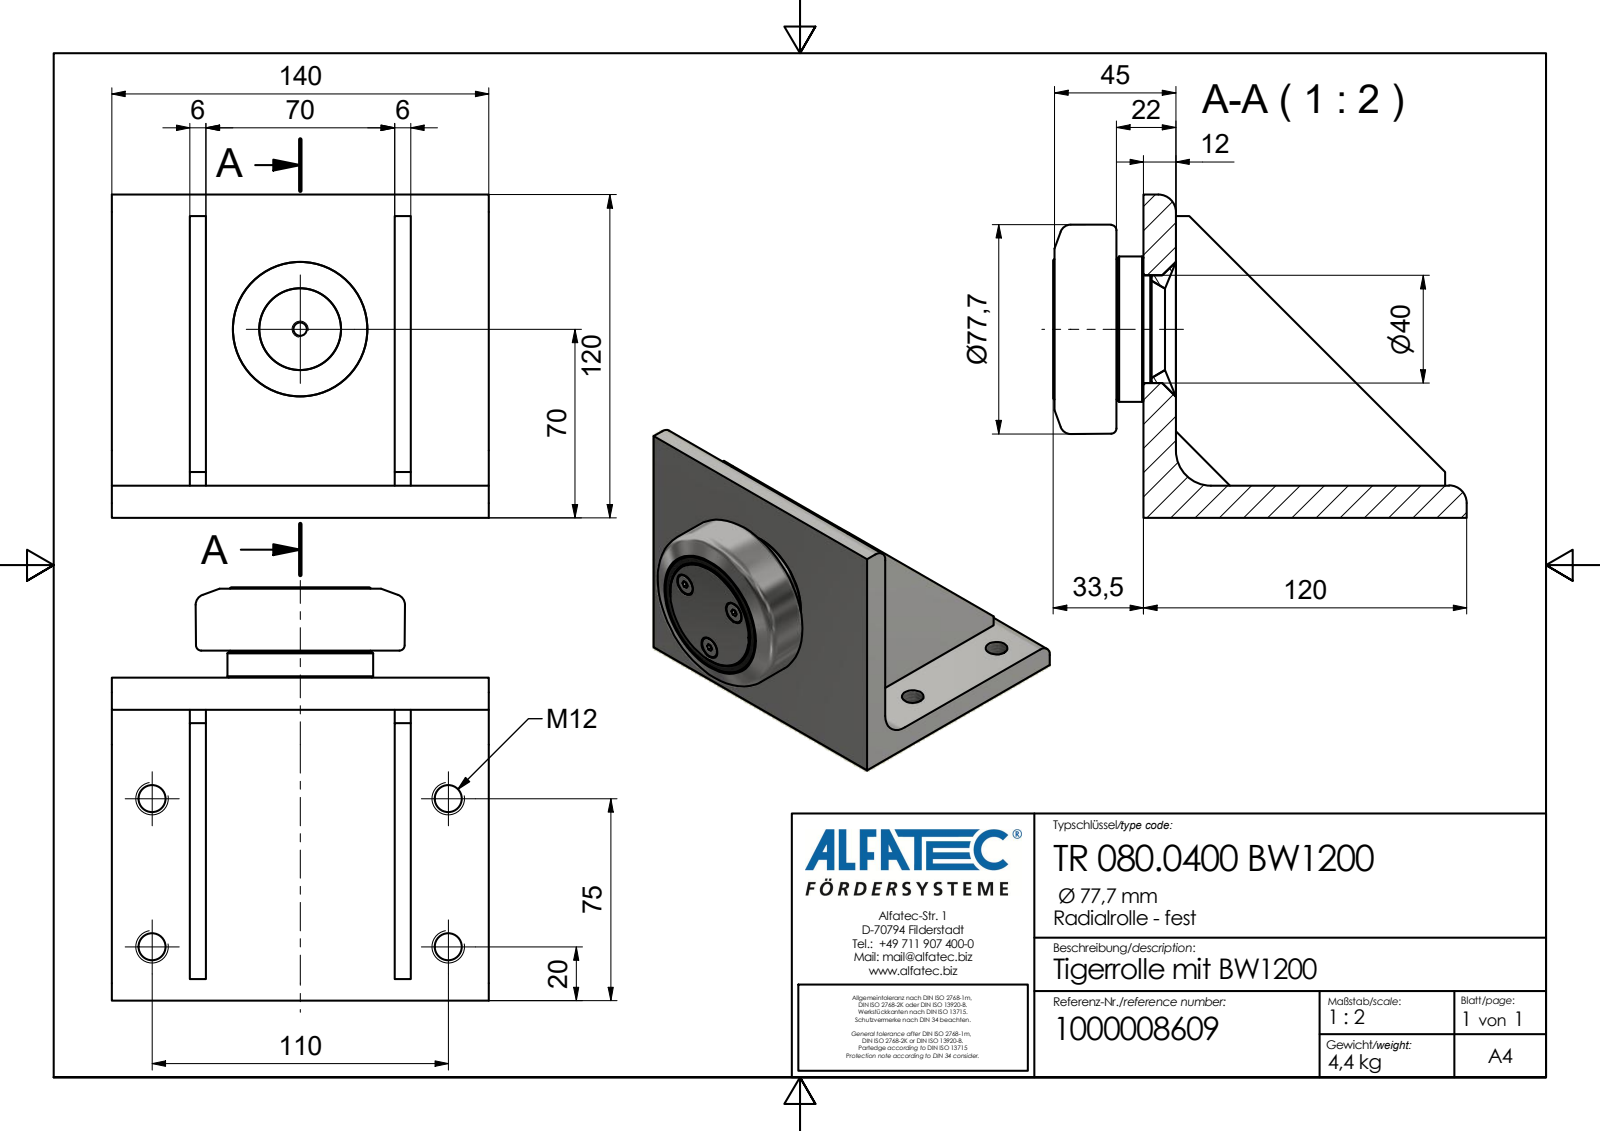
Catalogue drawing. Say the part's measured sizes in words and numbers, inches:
The part is named "TR 080.0400 BW1200_Kontur". Its 3-D file was written by "Autodesk Inventor 2020 (AP242_MANAGED_MODEL_BASED_3D_ENGINEERING_MIM_LF)". It is 1 solid with 78 faces: 53 planar, 17 cylindrical and 8 other. Overall it measures 6.043 by 5.512 by 4.724 inches. Its volume is 34.7 cubic inches and its surface area 163.4 square inches. Round holes: 4 of diameter 0.398, 3 of diameter 0.409, 1 of diameter 0.194. Round bosses or shafts: 3 of diameter 0.384, 1 of diameter 2.126, 1 of diameter 2.047. Partial cylindrical surfaces (rounded edges, fillets, slot ends): 2 of radius 0.256, 1 of radius 0.512. The main face-to-face distances are 0.472, 2.992, 0.236, 1.142, 1.378, 4.134, 4.37, 2.756, 3.228, 5.512. The hole center spacings are 0.728, 1.261, 2.165, 4.331, 4.842.
